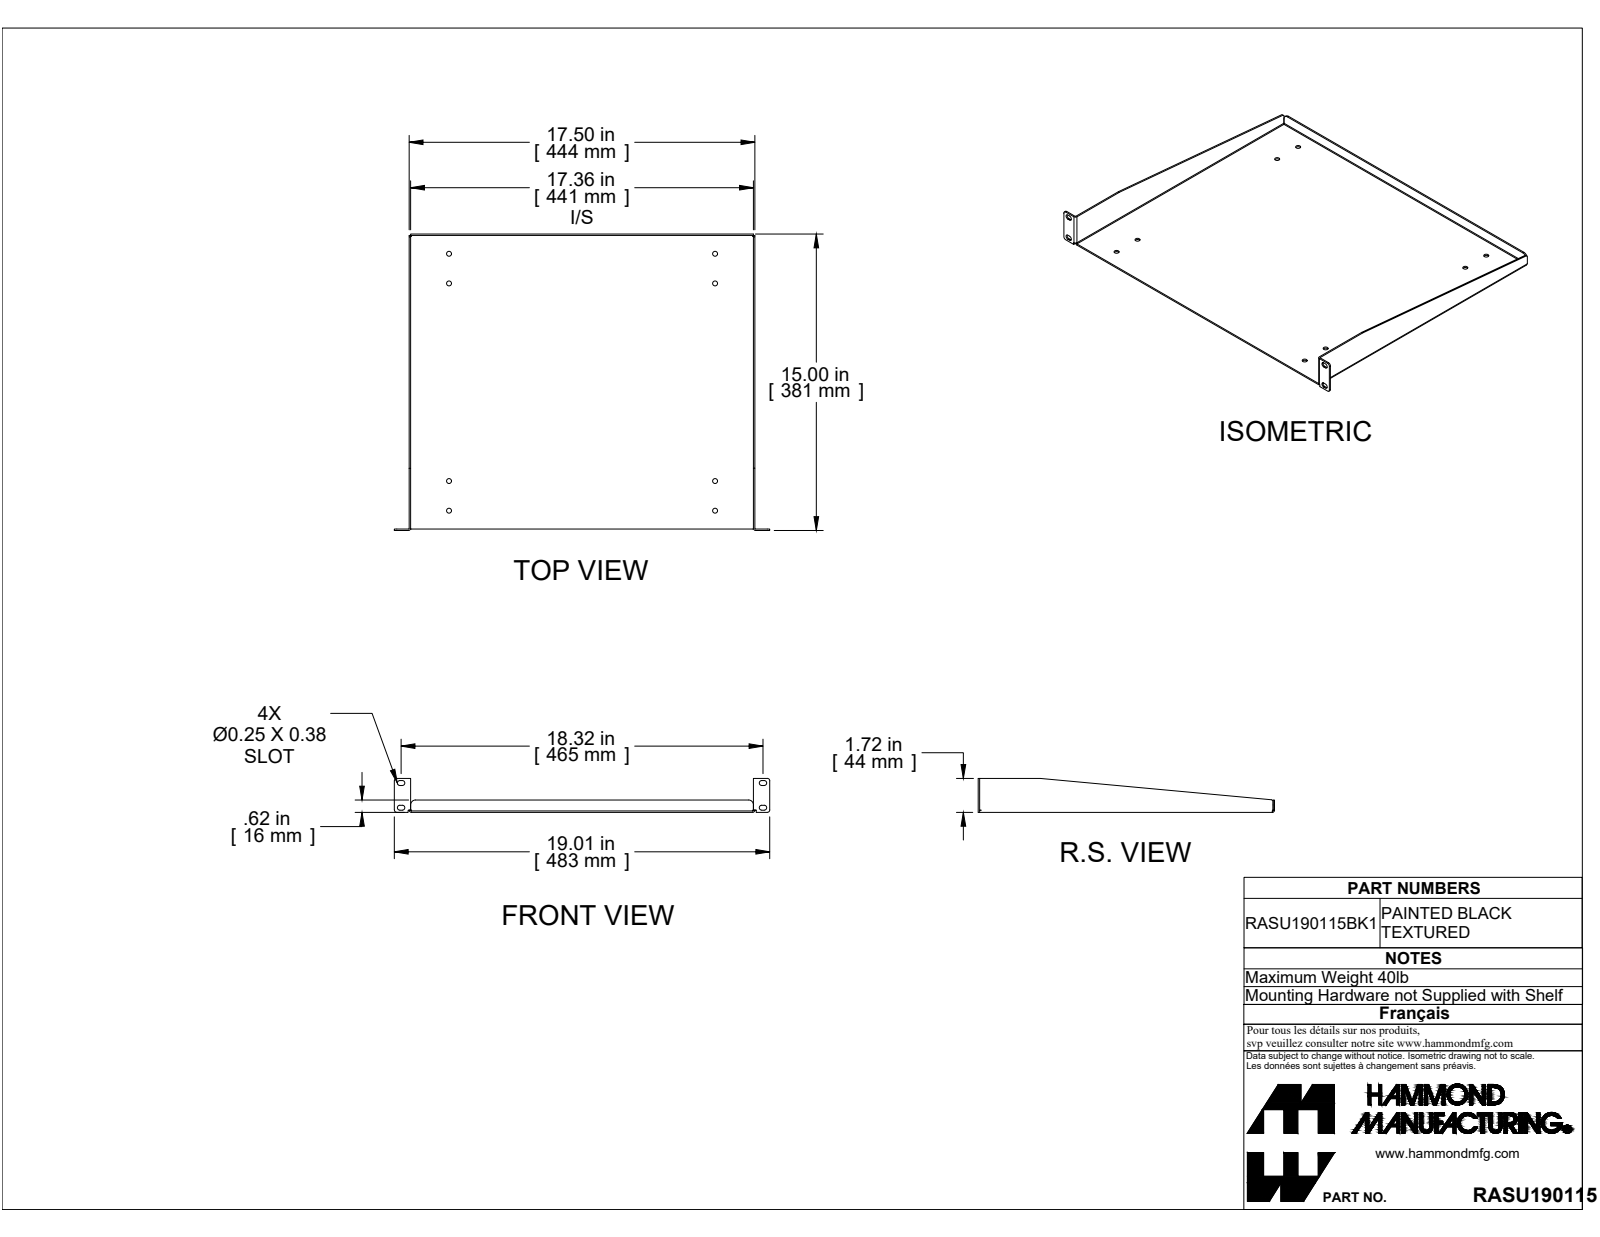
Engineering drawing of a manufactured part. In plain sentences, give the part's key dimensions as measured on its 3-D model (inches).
The part is named "RASU190115BK1". Its 3-D file was written by "SolidWorks 2019 (CONFIG_CONTROL_DESIGN)". It is 1 solid with 88 faces: 48 planar, 36 cylindrical and 4 other. Overall it measures 19.006 by 15 by 1.718 inches. Its volume is 22.13 cubic inches and its surface area 620.9 square inches. Round holes: 8 of diameter 0.25. Partial cylindrical surfaces (rounded edges, fillets, slot ends): 12 of radius 0.125, 5 of radius 0.036, 5 of radius 0.108, 3 of radius 0.055, 2 of radius 0.25. The main face-to-face distances are 0.072, 17.428, 17.356, 17.5, 14.856, 14.928, 0.072, 14.928, 15, 0.625. The hole center spacings are 1.5, 11.5, 13.468, 13.551, 17.709, 10, 13, 16.774.
